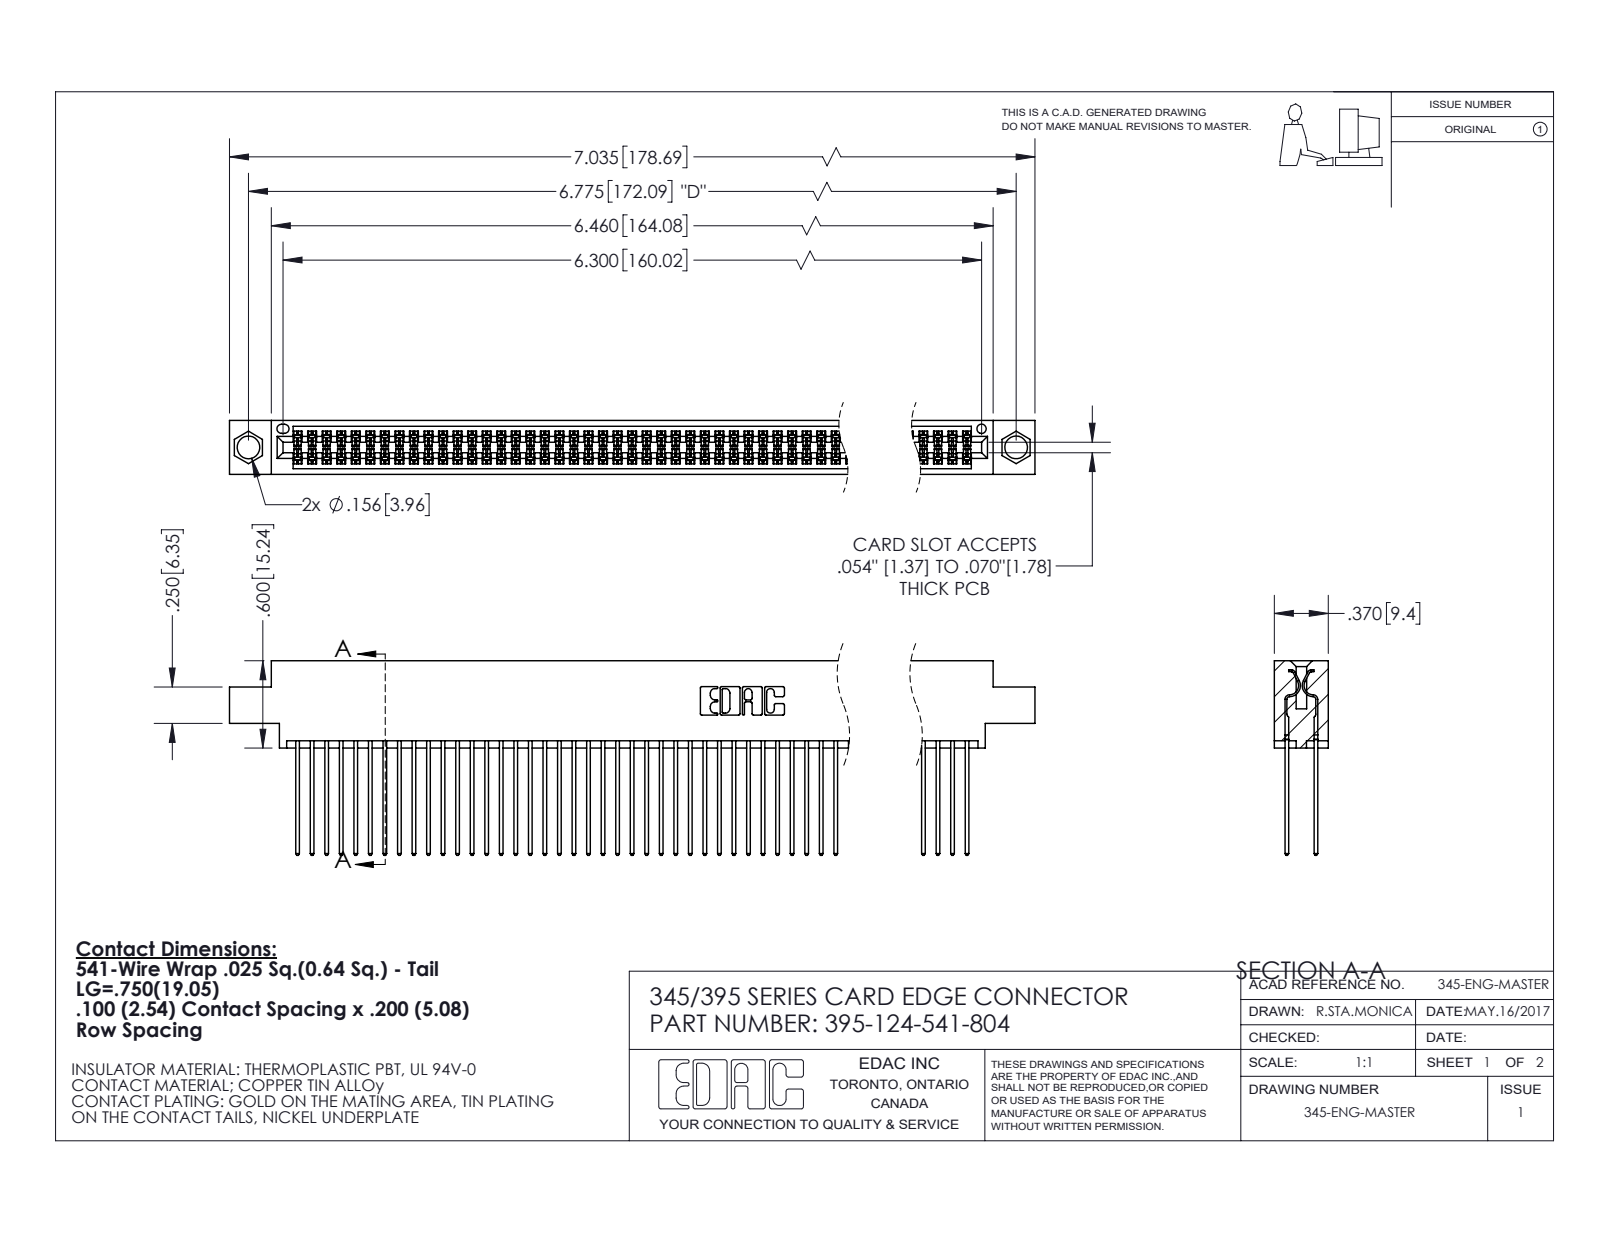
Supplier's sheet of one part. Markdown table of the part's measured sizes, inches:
| quantity | value |
| --- | --- |
| part name | 345 Part_0.170 Offset - 0.156 Dia-TI; 395-124-541-804; 345-292-001_345-293-141 |
| STEP written by | SolidWorks 2020 (CONFIG_CONTROL_DESIGN) |
| units | inches |
| bodies | 125 solids, 6344 faces (4190 planar, 2154 cylindrical, 0 other) |
| overall size | 7.035 × 1.337 × 0.37 |
| volume | 1.101 in³ |
| surface area | 47.1 in² |
| round holes (diameter × count) | 0.156 × 2, 0.064 × 1 |
| partial cylindrical surfaces (radius × count) | 0.006 × 186, 0.01 × 124, 0.01 × 22, 0.007 × 6, 0.031 × 6, 0.026 × 3, 0.014 × 2, 0.019 × 2 |
| main face-to-face distances | 0.072, 0.298, 0.2, 0.098, 0.272, 0.025, 0.225, 0.37, 0.175, 0.149 |
| hole center spacings | 0.27, 6.539, 6.775 |
